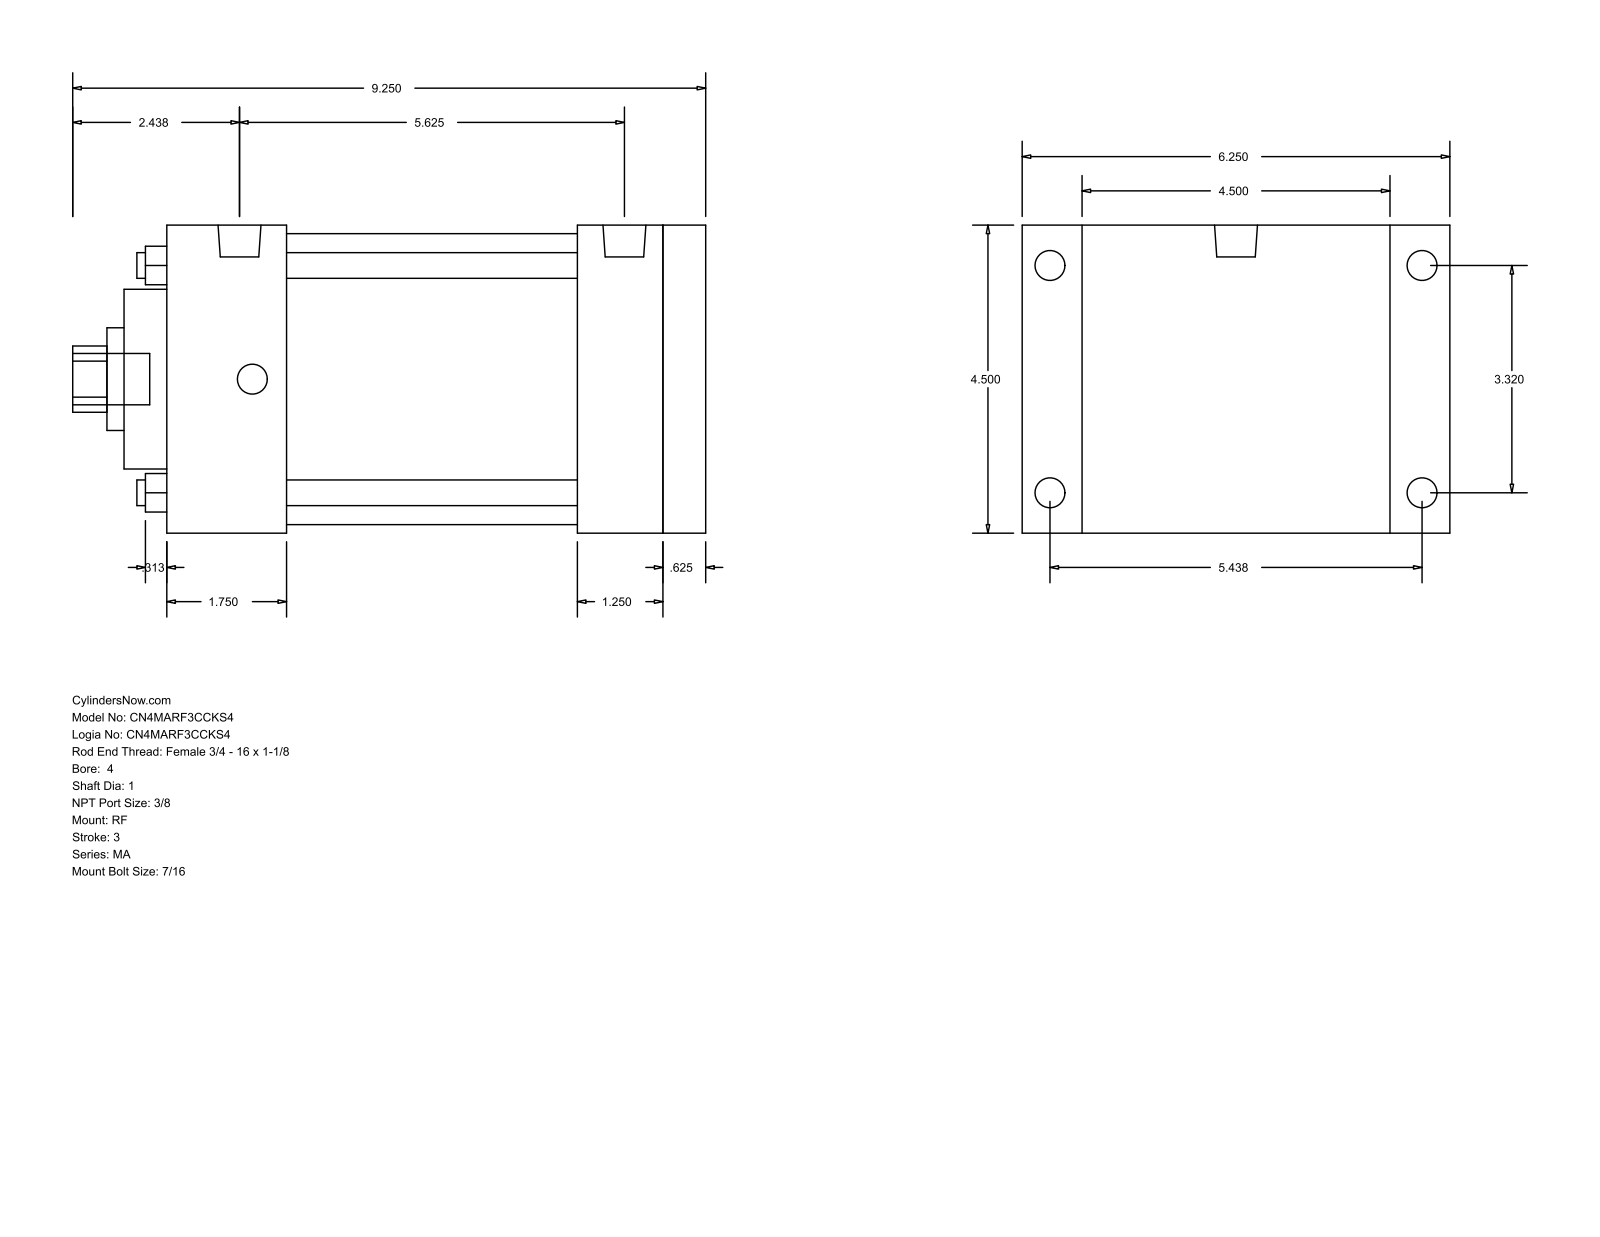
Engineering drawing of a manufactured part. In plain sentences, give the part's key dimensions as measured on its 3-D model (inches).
The part is named "MA_RF__0400_1". Its 3-D file was written by "GSSL Pune (CONFIG_CONTROL_DESIGN)". It is 0 solids with 94 faces: 65 planar, 29 cylindrical and 0 other. Overall it measures 9.25 by 6.25 by 4.5 inches. Round holes: 4 of diameter 0.375, 1 of diameter 1, 1 of diameter 1.5, 1 of diameter 2.625, 1 of diameter 4.25. Round bosses or shafts: 8 of diameter 0.437, 2 of diameter 0.627, 1 of diameter 0.75. Partial cylindrical surfaces (rounded edges, fillets, slot ends): 1 of radius 0.484. The main face-to-face distances are 4.5, 7.875, 7.25, 0.625, 0.875, 5.375, 6, 1.25, 1.875, 1.75. The hole center spacings are 2.347, 3.32, 4.695.
